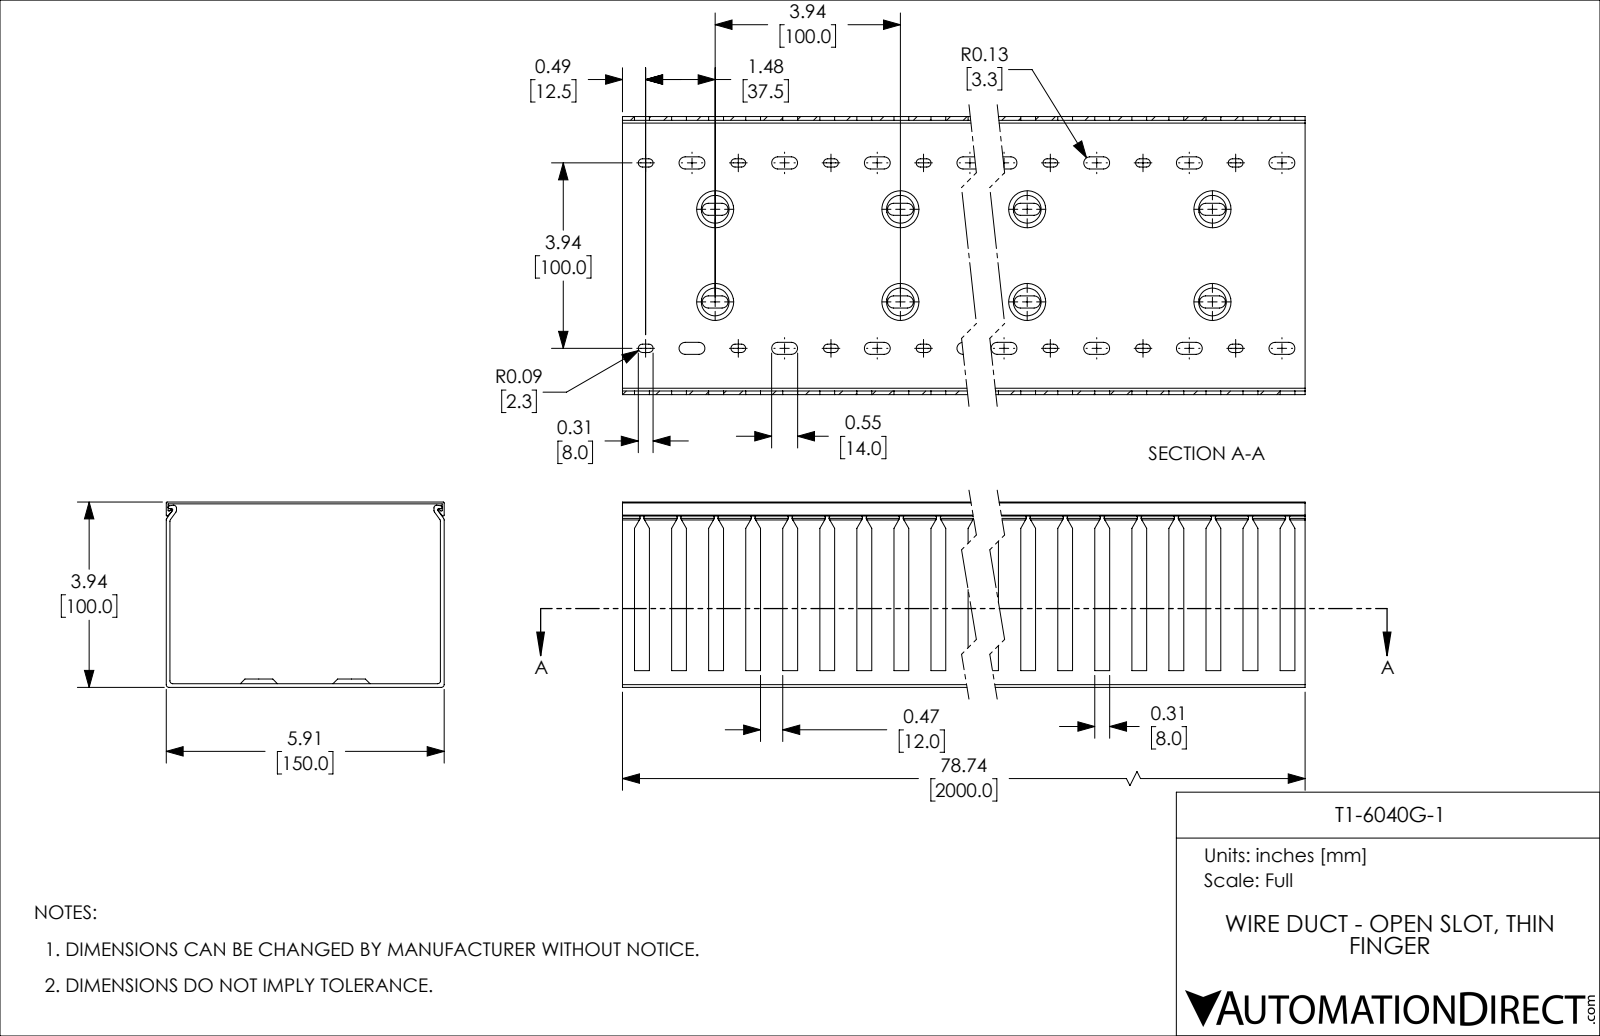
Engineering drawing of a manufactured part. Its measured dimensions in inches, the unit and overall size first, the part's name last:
Units: inches
Overall size (bounding box): 78.74 × 5.906 × 3.937
Partial cylindrical surfaces — rounded edges, fillets, slot ends (radius × count): R0.128 ×240, R0.089 ×160, R0.059 ×12, R0.02 ×8, R0.03 ×6
Main face-to-face distances: 0.079, 5.827, 0.039, 3.937, 3.898, 3.819, 3.858, 5.906, 5.748, 5.866
Volume: 103.4 in³ · Surface area: 3 159 in²
Bodies: 2 solids, 1661 faces (790 planar, 791 cylindrical, 80 other)
Part name (STEP PRODUCT): T1-6040G-1
STEP written by: SolidWorks 2021 (CONFIG_CONTROL_DESIGN)
